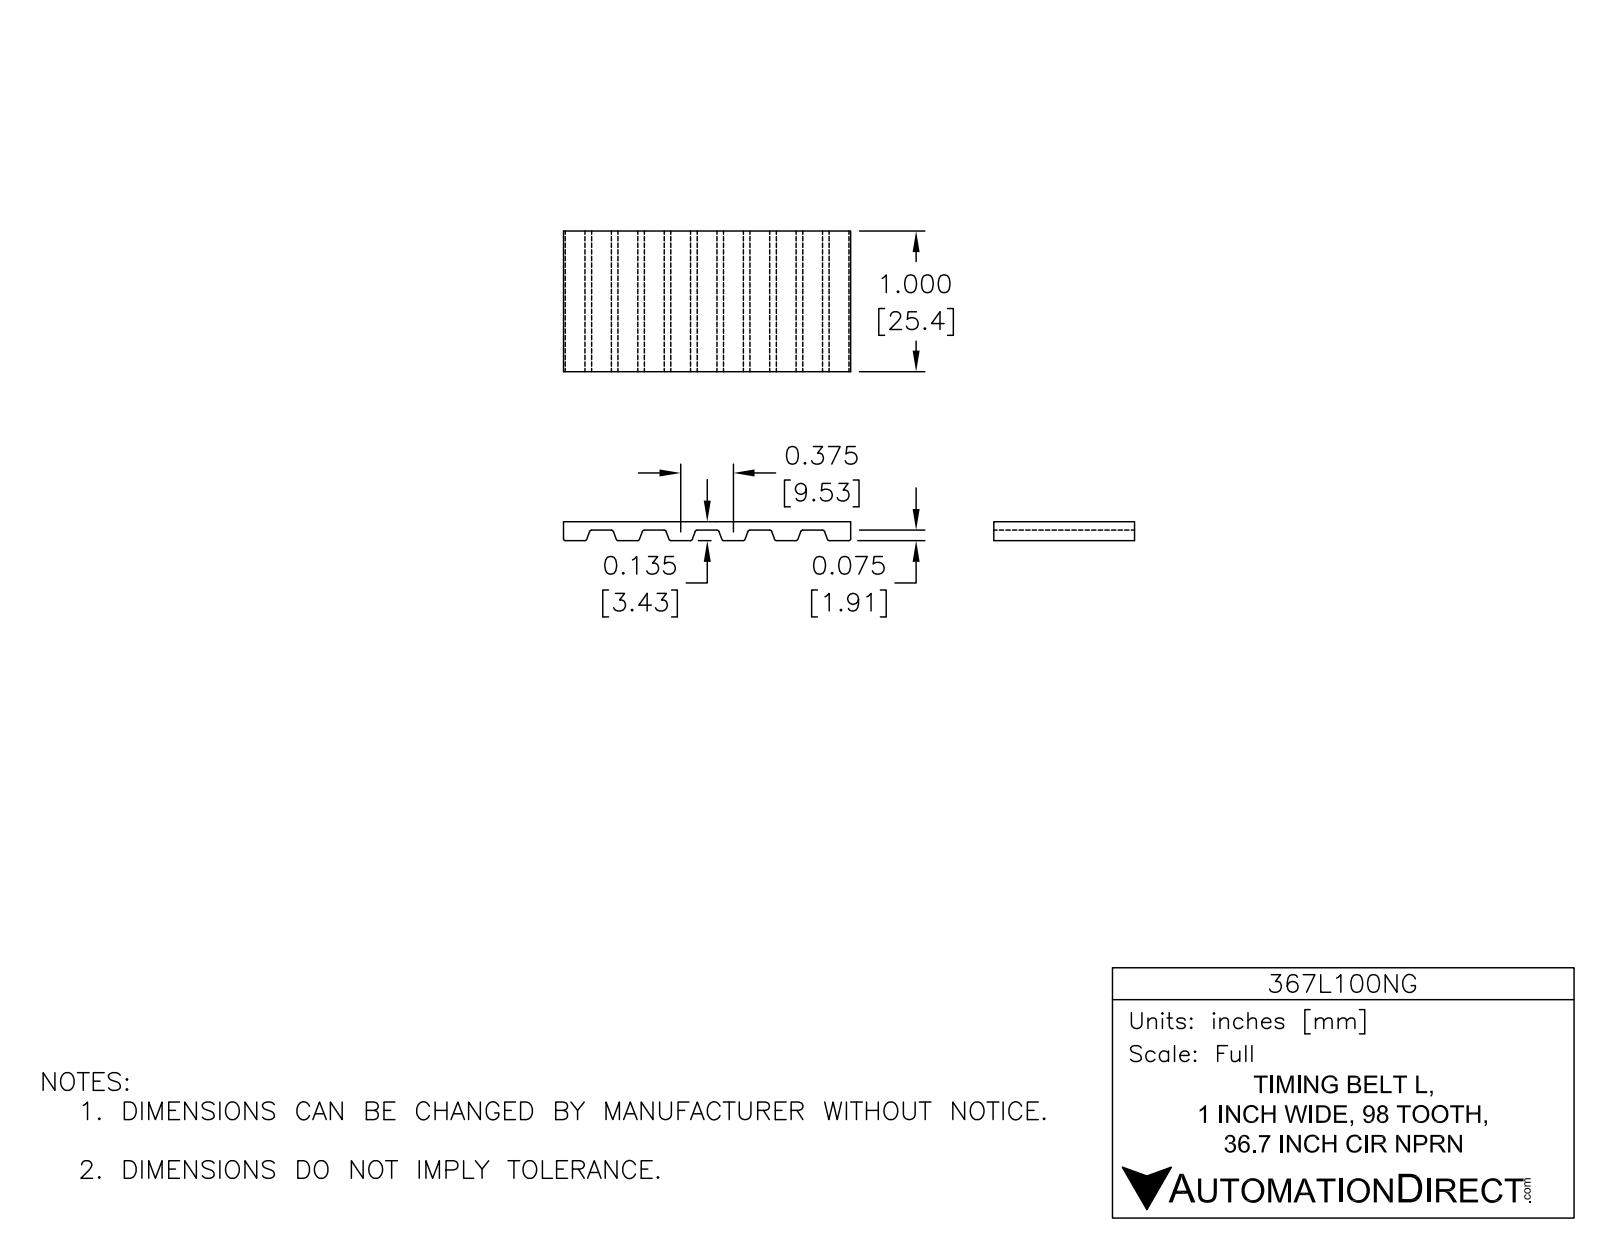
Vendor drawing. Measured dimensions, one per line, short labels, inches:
name: 367L100NG
written by: SolidWorks 2014 (AUTOMOTIVE_DESIGN)
unit: in
bodies: 1 solid, 798 faces (369 planar, 429 cylindrical, 0 other)
size: 16.663 × 3 × 1
volume: 3.329 in³; area: 88.54 in²
rounds: 388× R0.02, 2× R1.435, 2× R1.5
face distances: 0.065, 2.935, 3, 2.87, 0.14, 2.86, 0.075, 2.795, 1, 2.72
